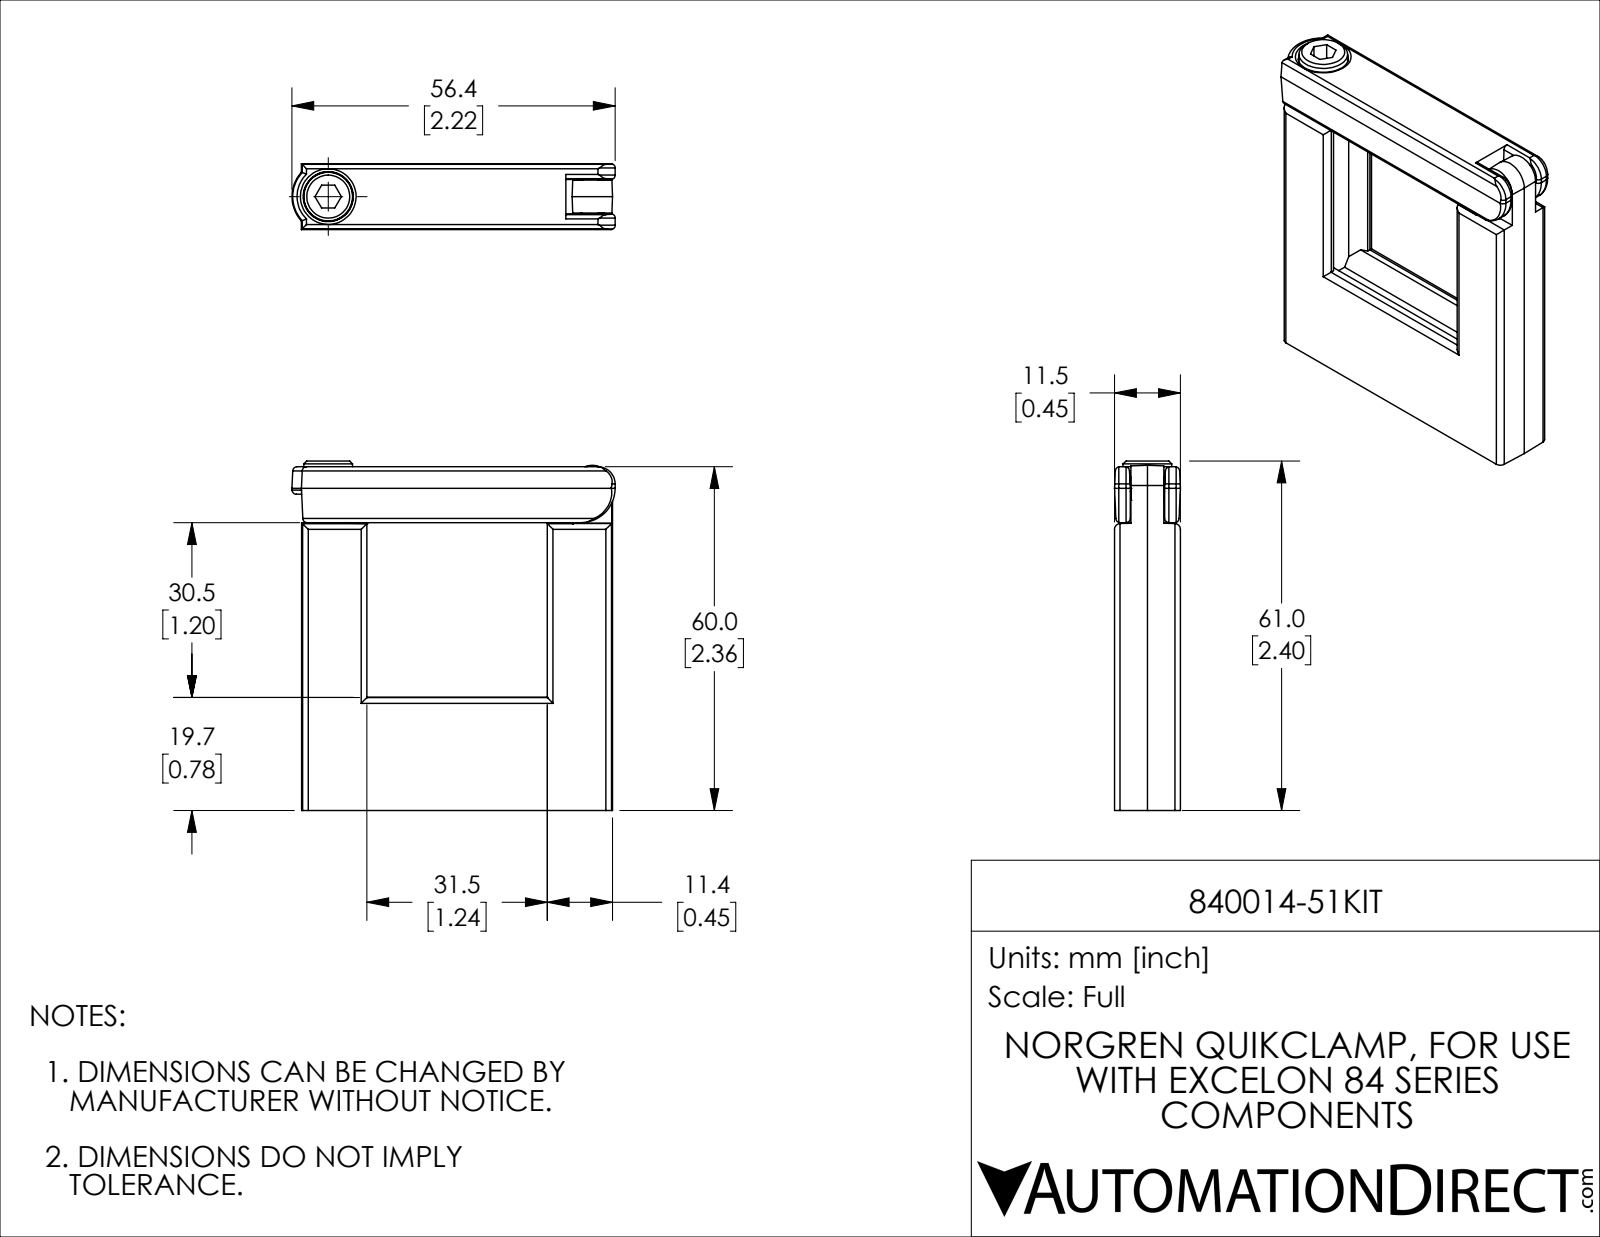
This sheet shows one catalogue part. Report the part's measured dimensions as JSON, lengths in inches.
{"part_name": "840014-51KIT", "step_written_by": "SolidWorks 2021 (CONFIG_CONTROL_DESIGN)", "units": "inches", "bodies": {"solids": 1, "faces": 171, "planar": 93, "cylindrical": 46, "other": 32}, "overall_size": [2.402, 2.222, 0.453], "volume_in3": 1.296, "surface_area_in2": 16.82, "round_holes": [[0.194, 1]], "round_bosses_or_shafts": [[0.335, 1], [0.197, 1]], "partial_cylinders_radius": [[0.039, 16], [0.03, 14], [0.077, 1], [0.083, 1], [0.118, 1], [0.236, 1]], "face_to_face_distances": [0.453, 2.135, 0.384, 1.978, 2.362, 0.452, 0.908, 0.472, 1.506, 1.89]}
